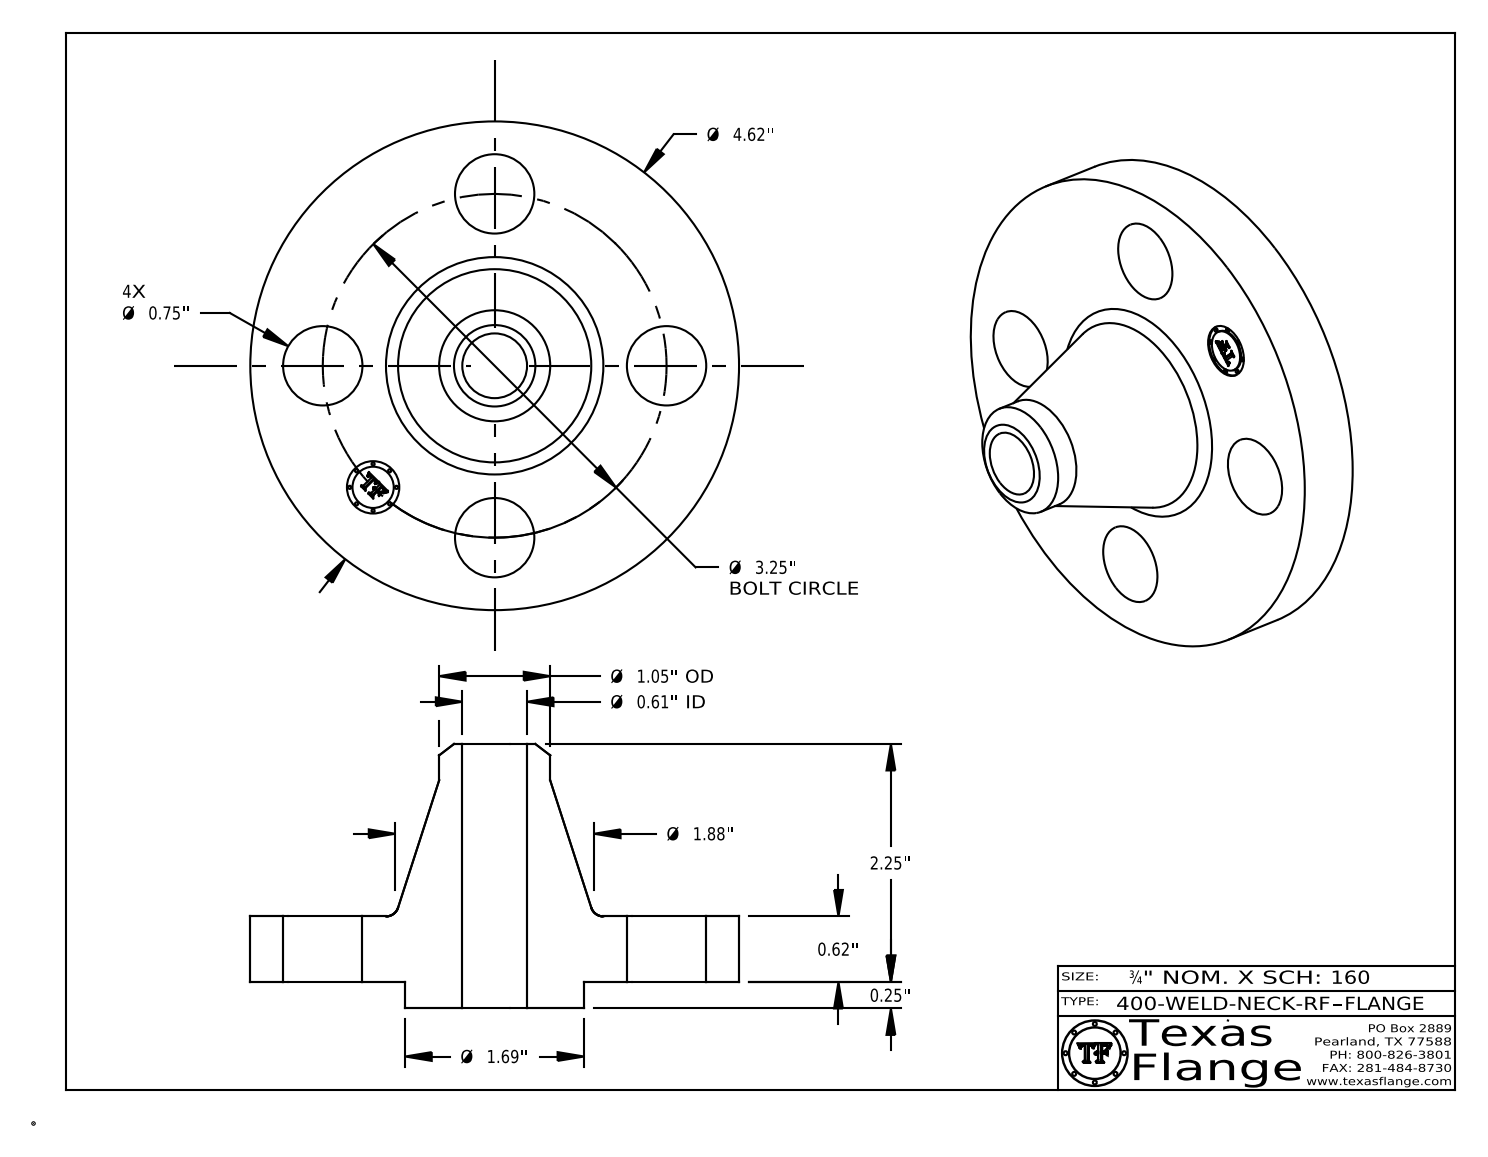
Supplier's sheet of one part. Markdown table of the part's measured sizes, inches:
| quantity | value |
| --- | --- |
| part name | 400-WELD-NECK-RF |
| STEP written by | CATIA V5 STEP AP214 (AUTOMOTIVE_DESIGN) |
| units | inches |
| bodies | 1 solid, 411 faces (369 planar, 36 cylindrical, 6 other) |
| overall size | 4.62 × 4.62 × 2.5 |
| volume | 11.63 in³ |
| surface area | 55.53 in² |
| round holes (diameter × count) | 0.75 × 4, 0.495 × 1, 0.612 × 1 |
| round bosses / shafts (diameter × count) | 0.03 × 8, 4.62 × 1, 1.69 × 1, 1.05 × 1, 0.39 × 1 |
| main face-to-face distances | 0.62, 0.25, 0.87, 2.5, 2.25, 1.63, 0.855, 0.605, 0.015, 1.645 |
| hole center spacings | 1.625, 2.298, 1.244, 3.003, 3.25 |
